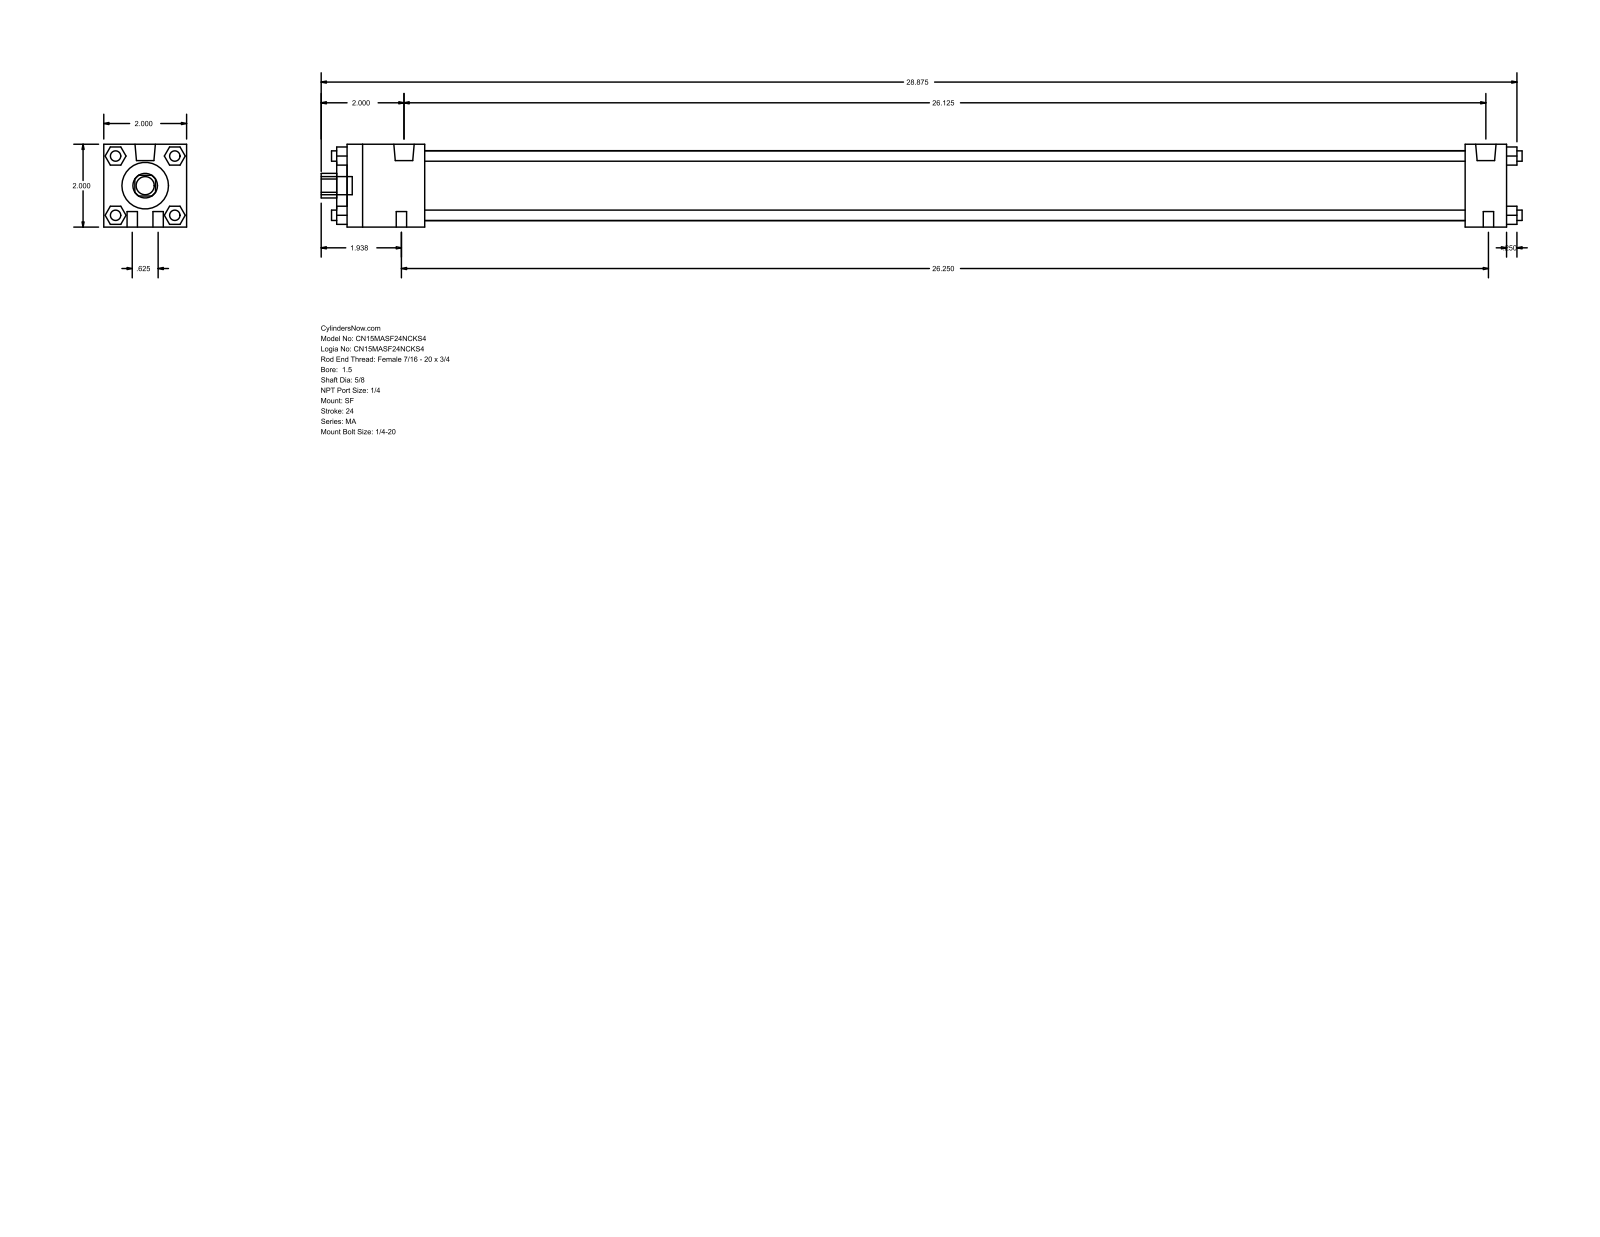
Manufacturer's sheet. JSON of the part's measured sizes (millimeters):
{"part_name": "MA_SF__0150_0.625", "step_written_by": "GSSL Pune (CONFIG_CONTROL_DESIGN)", "units": "millimeters", "bodies": {"solids": 0, "faces": 124, "planar": 94, "cylindrical": 30, "other": 0}, "overall_size": [736.6, 50.8, 50.8], "round_holes": [[15.88, 1], [28.57, 1], [42.93, 1]], "round_bosses_or_shafts": [[6.35, 8], [12.49, 2], [7.94, 2], [11.11, 1]], "partial_cylinders_radius": [[7.54, 1]], "face_to_face_distances": [50.8, 711.2, 47.62, 685.79, 638.17, 663.58, 25.41, 6.35, 717.55, 53.97]}
